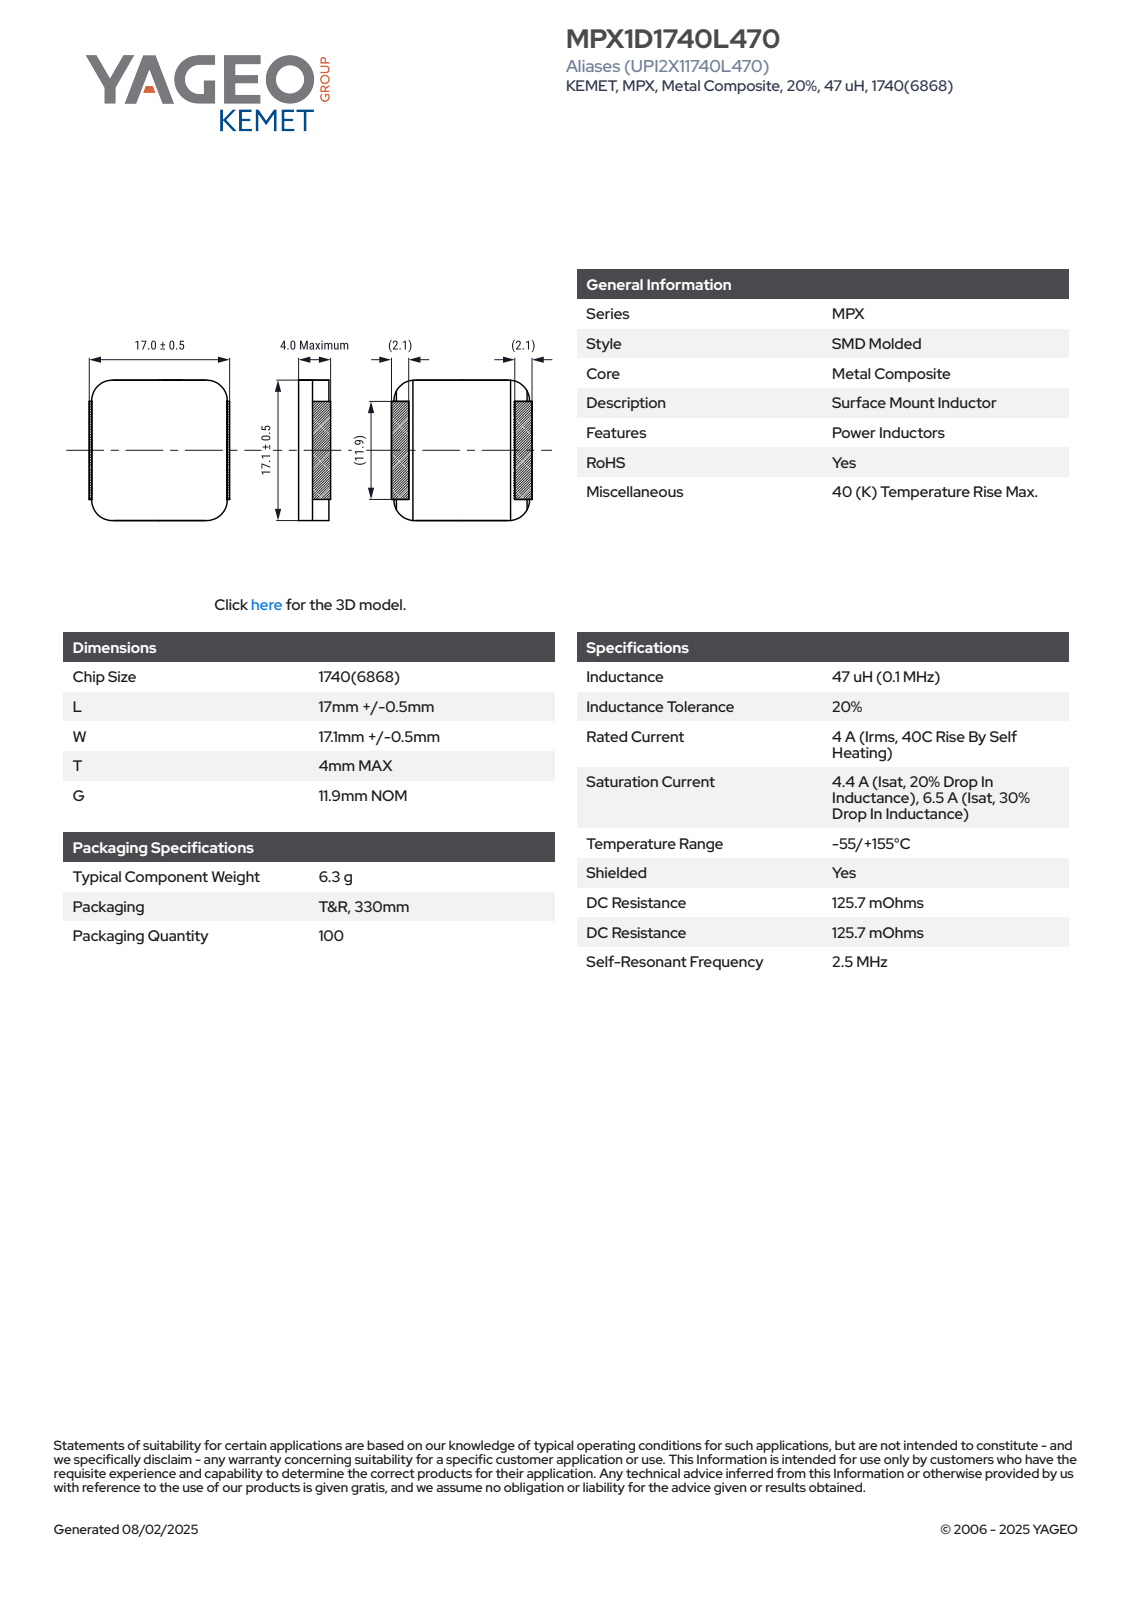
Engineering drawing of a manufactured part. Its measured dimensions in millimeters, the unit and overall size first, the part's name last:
Units: millimetres
Overall size (bounding box): 17.6 × 17.5 × 4
Partial cylindrical surfaces — rounded edges, fillets, slot ends (radius × count): R0.3 ×4, R2.5 ×4, R2.5 ×4
Main face-to-face distances: 3.9, 0.5, 16.7, 3.7, 16.2, 17.6, 4, 0.8, 17, 17.2
Volume: 1 111 mm³ · Surface area: 950 mm²
Bodies: 1 solid, 122 faces (104 planar, 18 cylindrical, 0 other)
Part name (STEP PRODUCT): MPX1D1740(KEMET)
STEP written by: SolidWorks 2018 (AUTOMOTIVE_DESIGN)
